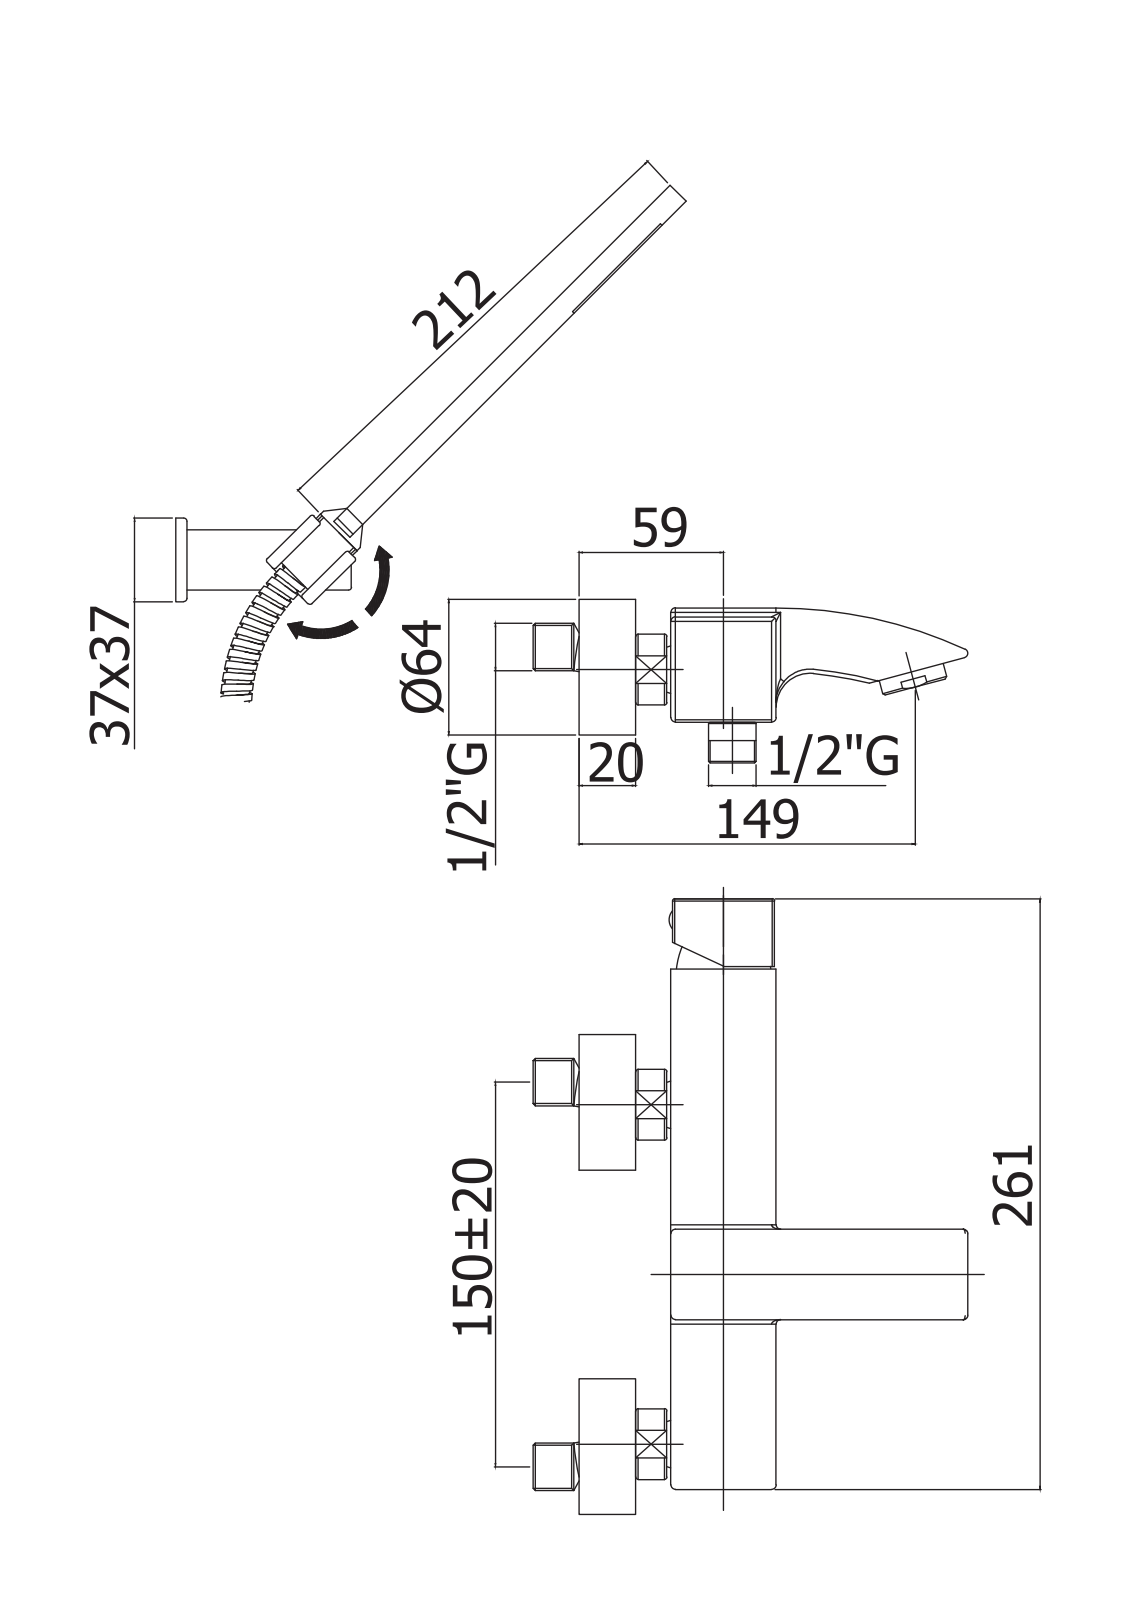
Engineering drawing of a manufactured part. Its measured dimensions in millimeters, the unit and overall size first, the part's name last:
Units: millimetres
Overall size (bounding box): 447.5 × 330.5 × 166.24
Round holes (diameter × count): ⌀7 ×4, ⌀24.5 ×3, ⌀25 ×3, ⌀4 ×2, ⌀10.5 ×2, ⌀11 ×2, ⌀16.5 ×2, ⌀18 ×2, ⌀21 ×2, ⌀21.6 ×2, ⌀28.5 ×2, ⌀31 ×2
Round bosses / shafts (diameter × count): ⌀2 ×11, ⌀27 ×3, ⌀24 ×3, ⌀63.5 ×2, ⌀28 ×2, ⌀37 ×1, ⌀35.5 ×1, ⌀35 ×1
Partial cylindrical surfaces — rounded edges, fillets, slot ends (radius × count): R1 ×42, R0.5 ×33, R2 ×15, R0.15 ×11, R0.3 ×4, R4 ×2, R15.6 ×2, R3 ×1
Main face-to-face distances: 3.75, 42.75, 46.5, 18.75, 39, 15, 24, 25, 3, 27.75
Hole centre spacings: 7.07, 8.6, 11.4, 4, 6, 10, 14, 14.1
Volume: 504 955 mm³ · Surface area: 251 839 mm²
Bodies: 3 solids, 3326 faces (2511 planar, 462 cylindrical, 353 other)
Part name (STEP PRODUCT): LEC023CR
STEP written by: CREO PARAMETRIC BY PTC INC, 2020044 (CONFIG_CONTROL_DESIGN)
